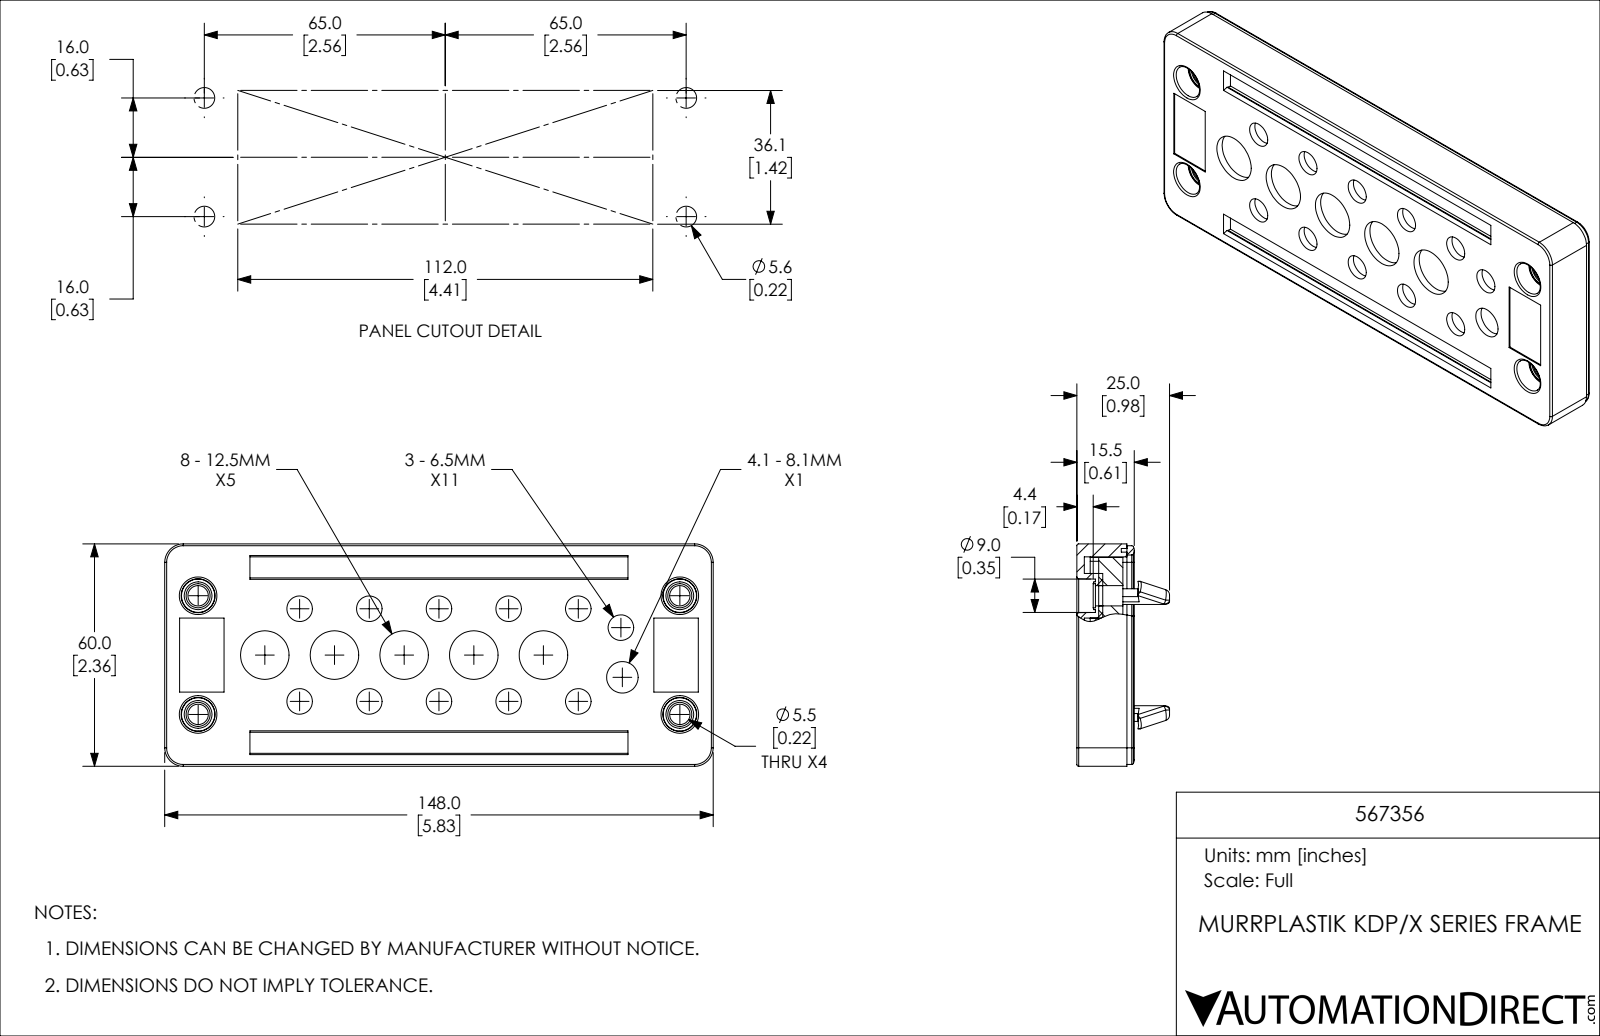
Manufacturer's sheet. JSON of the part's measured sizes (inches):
{"part_name": "567356", "step_written_by": "SolidWorks 2019 (CONFIG_CONTROL_DESIGN)", "units": "inches", "bodies": {"solids": 4, "faces": 438, "planar": 162, "cylindrical": 224, "other": 52}, "overall_size": [5.827, 2.362, 0.984], "volume_in3": 4.95, "surface_area_in2": 101.2, "round_holes": [[0.272, 11], [0.433, 11], [0.516, 5], [0.673, 5], [0.217, 4], [0.256, 4], [0.335, 1], [0.5, 1]], "round_bosses_or_shafts": [[0.295, 4]], "partial_cylinders_radius": [[0.059, 20], [0.02, 12], [0.079, 12], [0.039, 8], [0.118, 8], [0.108, 4], [0.128, 4], [0.138, 4]], "face_to_face_distances": [0.091, 0.232, 0.142, 0.256, 0.488, 0.346, 0.079, 0.063, 0.154, 0.409], "hole_center_spacings": [0.616, 1.215, 0.74, 1.915, 1.48, 1.231, 1.778, 2.22]}
